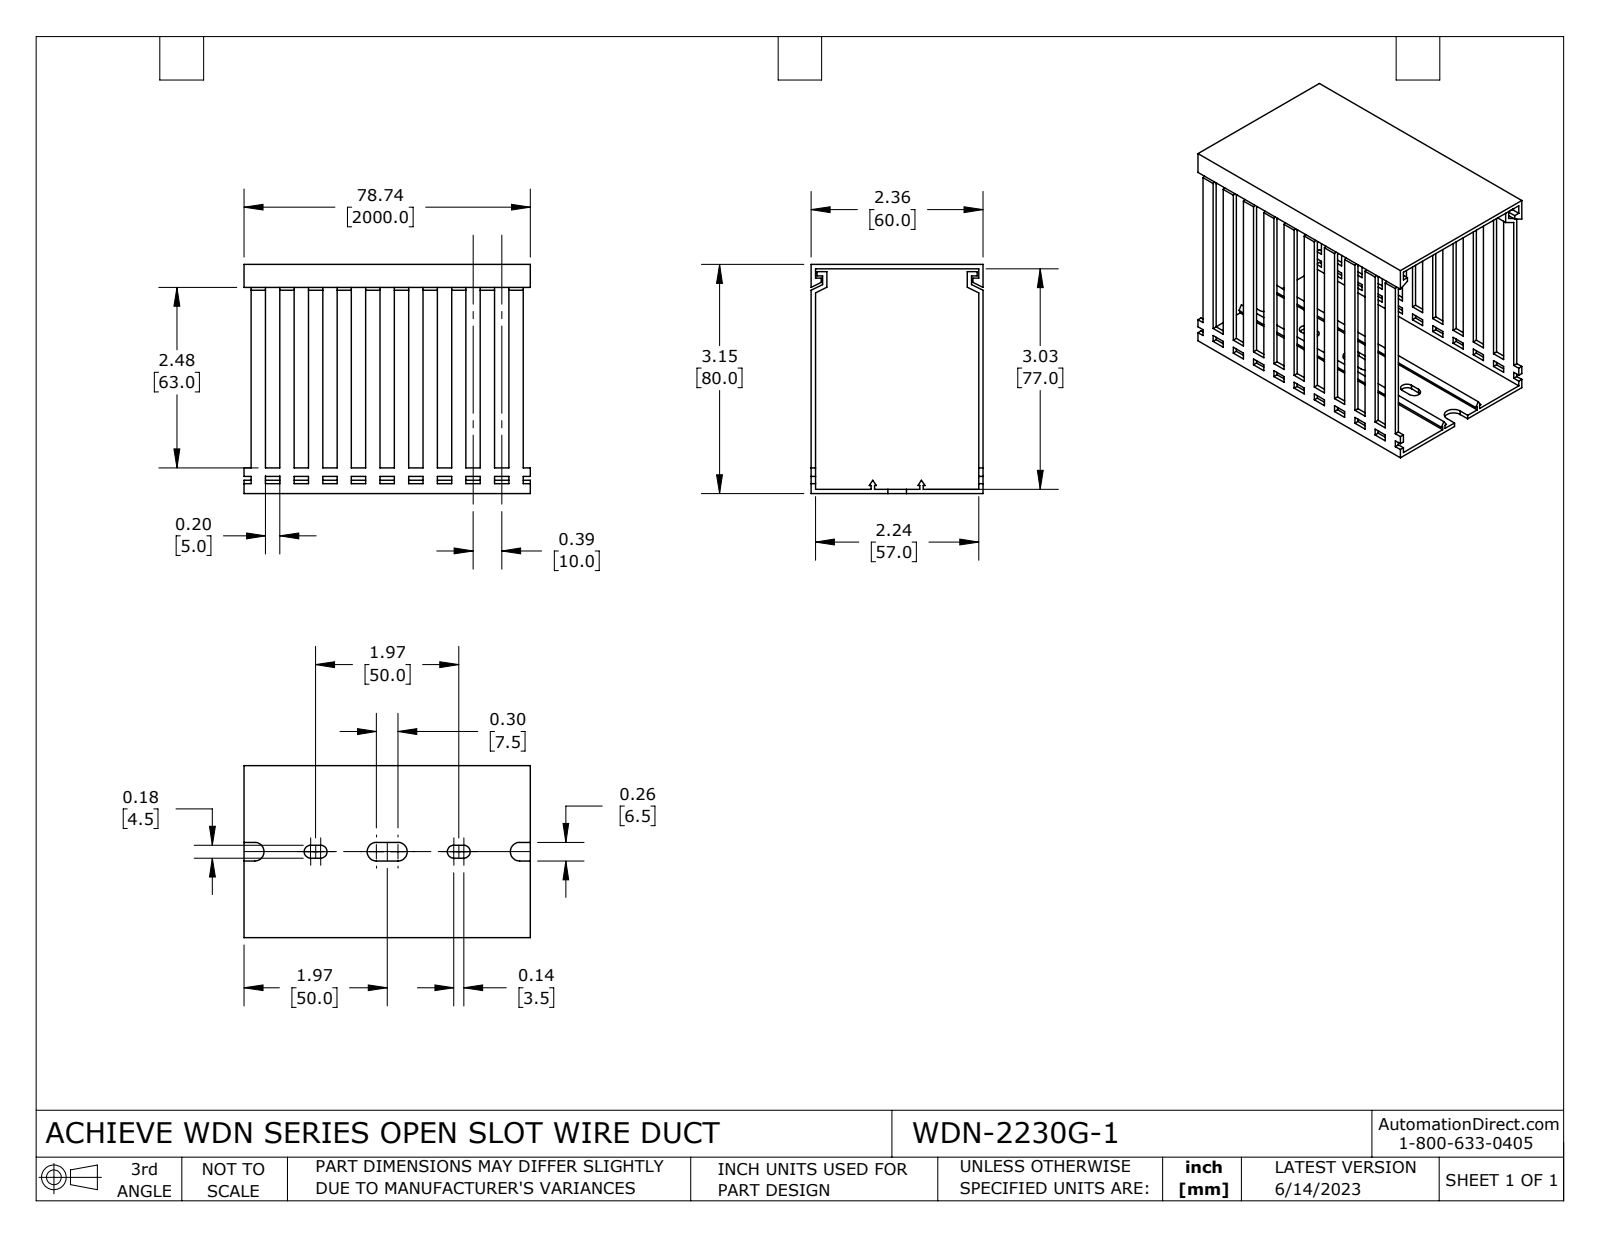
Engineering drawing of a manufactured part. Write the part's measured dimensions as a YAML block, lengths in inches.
part_name: "WDN-2230G-1"
step_written_by: "SolidWorks 2021 (CONFIG_CONTROL_DESIGN)"
units: inches
bodies: {solids: 2, faces: 336, planar: 324, cylindrical: 12, other: 0}
overall_size: [3.937, 3.15, 2.362]
volume: 2.021
surface_area: 77.18
partial_cylinders:
  - {radius: 0.089, count: 4}
  - {radius: 0.128, count: 4}
face_to_face_distances: [0.059, 3.091, 2.303, 3.15, 2.362, 3.031, 0.197, 0.394, 2.244, 0.591]
